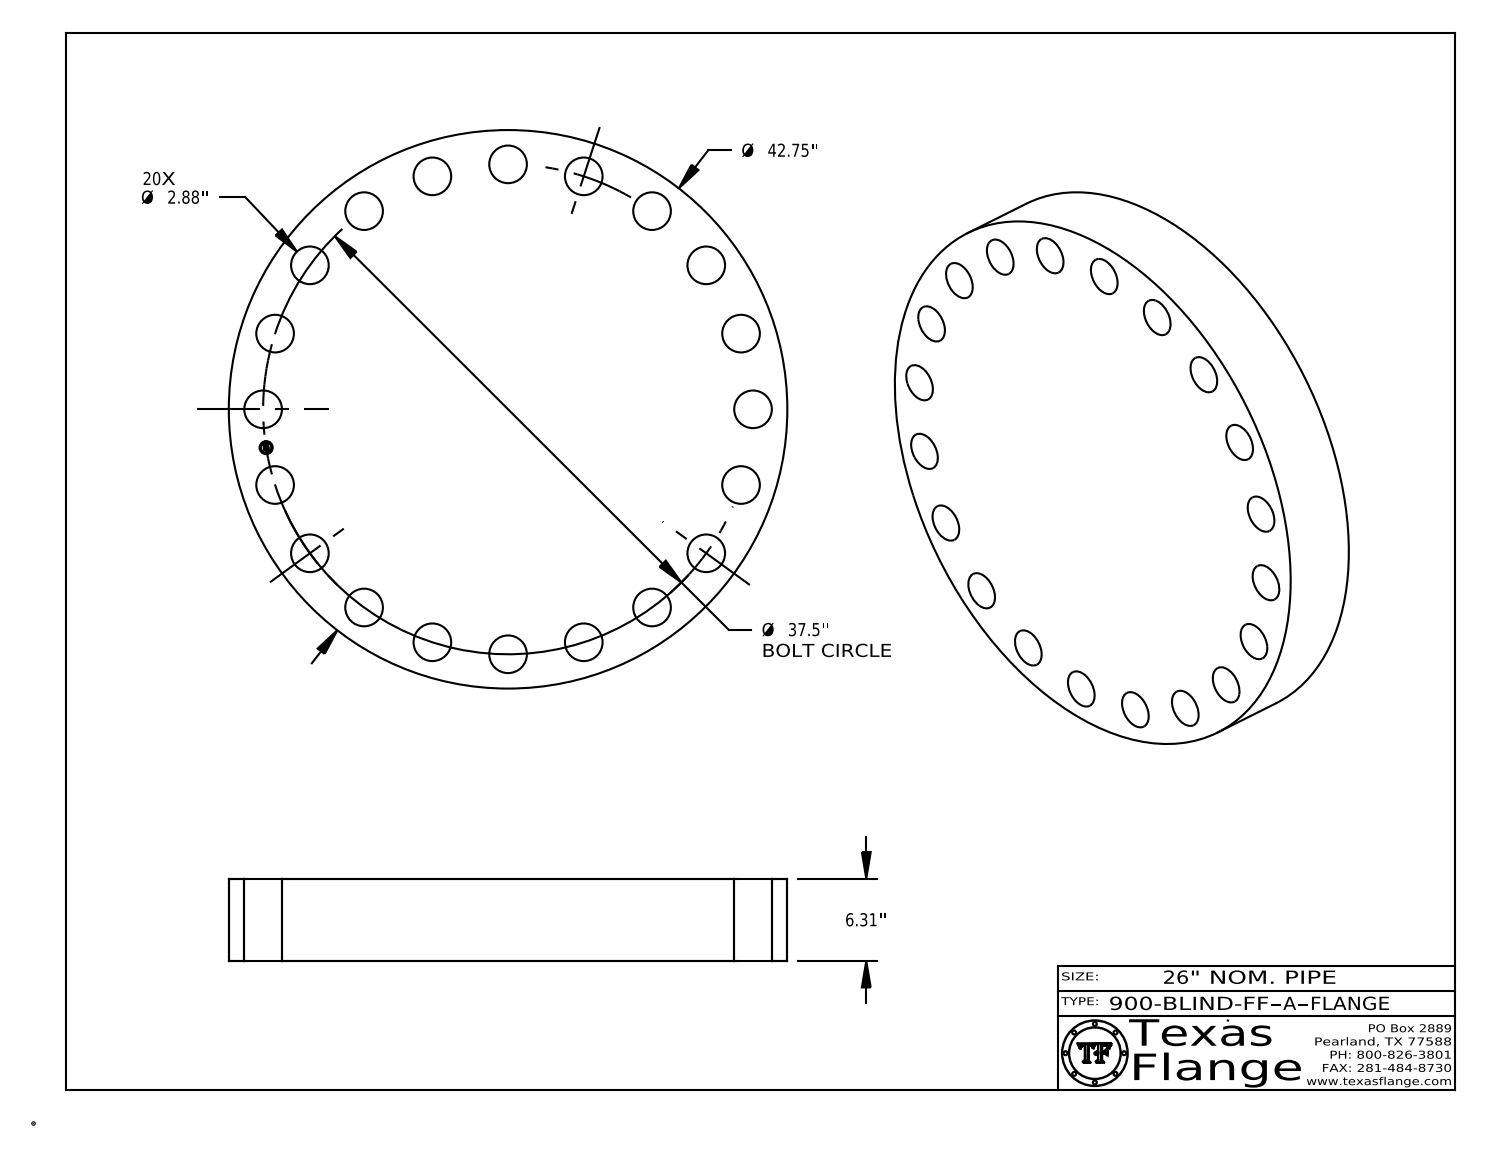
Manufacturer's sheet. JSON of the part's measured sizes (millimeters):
{"part_name": "900-BLIND-FF, Series A", "step_written_by": "CATIA V5 STEP AP214 (AUTOMOTIVE_DESIGN)", "units": "millimeters", "bodies": {"solids": 1, "faces": 429, "planar": 367, "cylindrical": 62, "other": 0}, "overall_size": [1085.9, 1085.9, 160.3], "volume_mm3": 134900000, "surface_area_mm2": 2968000, "round_holes": [[73.2, 20], [25.4, 1]], "round_bosses_or_shafts": [[1.5, 8], [1085.9, 1], [20, 1]], "face_to_face_distances": [160.3, 0.4, 159.9, 7.6, 7.4, 1.4, 4.9, 6.3, 1.1, 3.8], "hole_center_spacings": [149, 294.3, 432.4, 559.9, 848.7, 905.9, 940.8, 673.5]}
